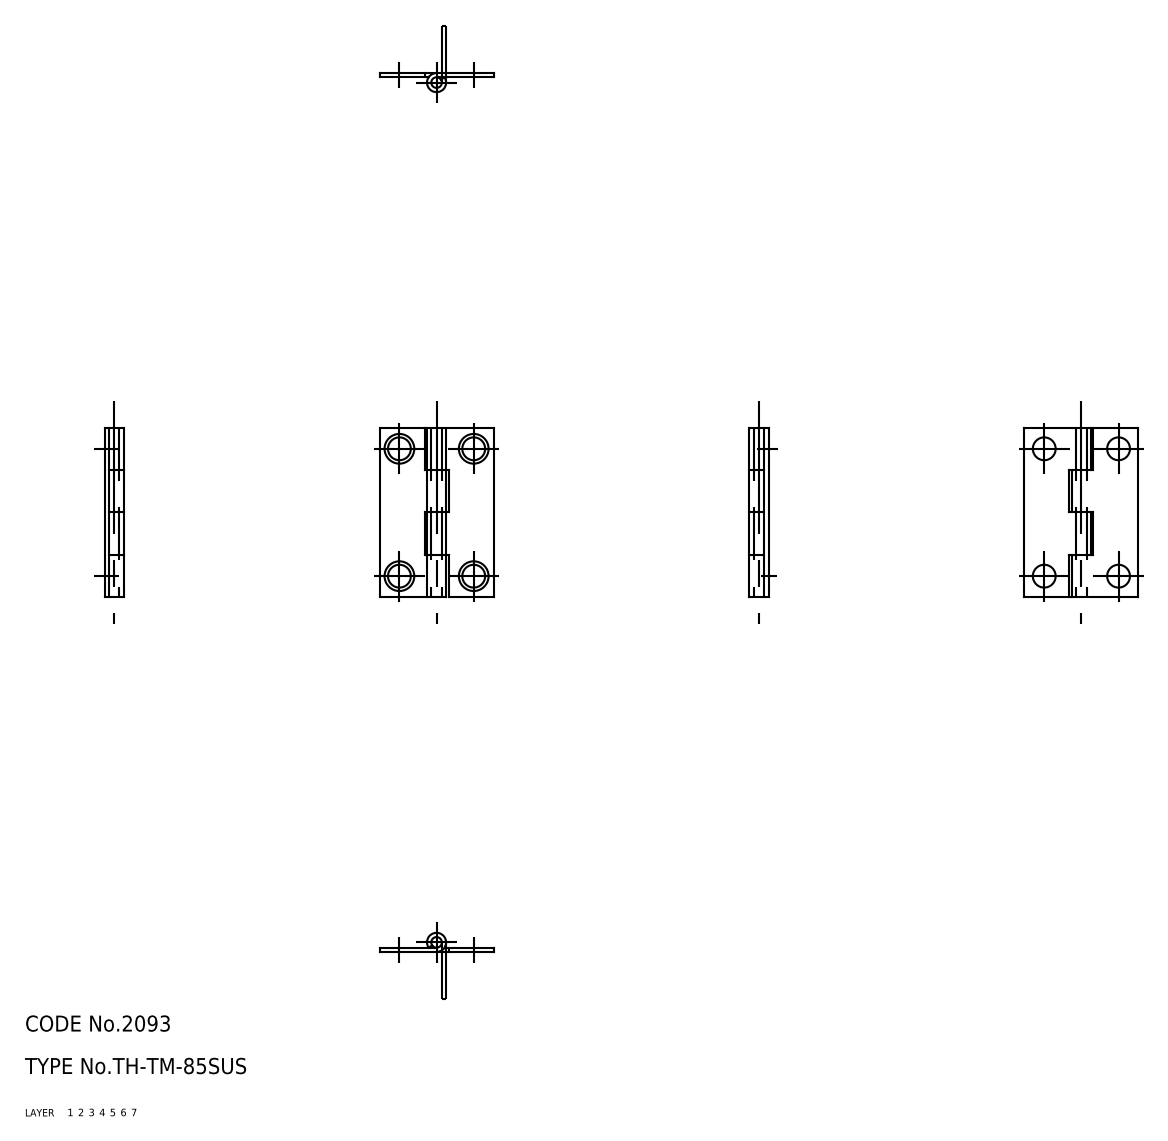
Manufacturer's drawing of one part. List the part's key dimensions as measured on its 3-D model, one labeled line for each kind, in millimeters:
Part name (STEP PRODUCT): shaft; hinge piece_B; hinge piece_A; TH_TM_85SUS_26183_36
STEP written by: CADfix (AUTOMOTIVE_DESIGN)
Units: millimetres
Bodies: 3 solids, 52 faces (0 planar, 0 cylindrical, 52 other)
Overall size (bounding box): 32 × 21.5 × 3.6
Volume: 723 mm³ · Surface area: 2 012 mm²
